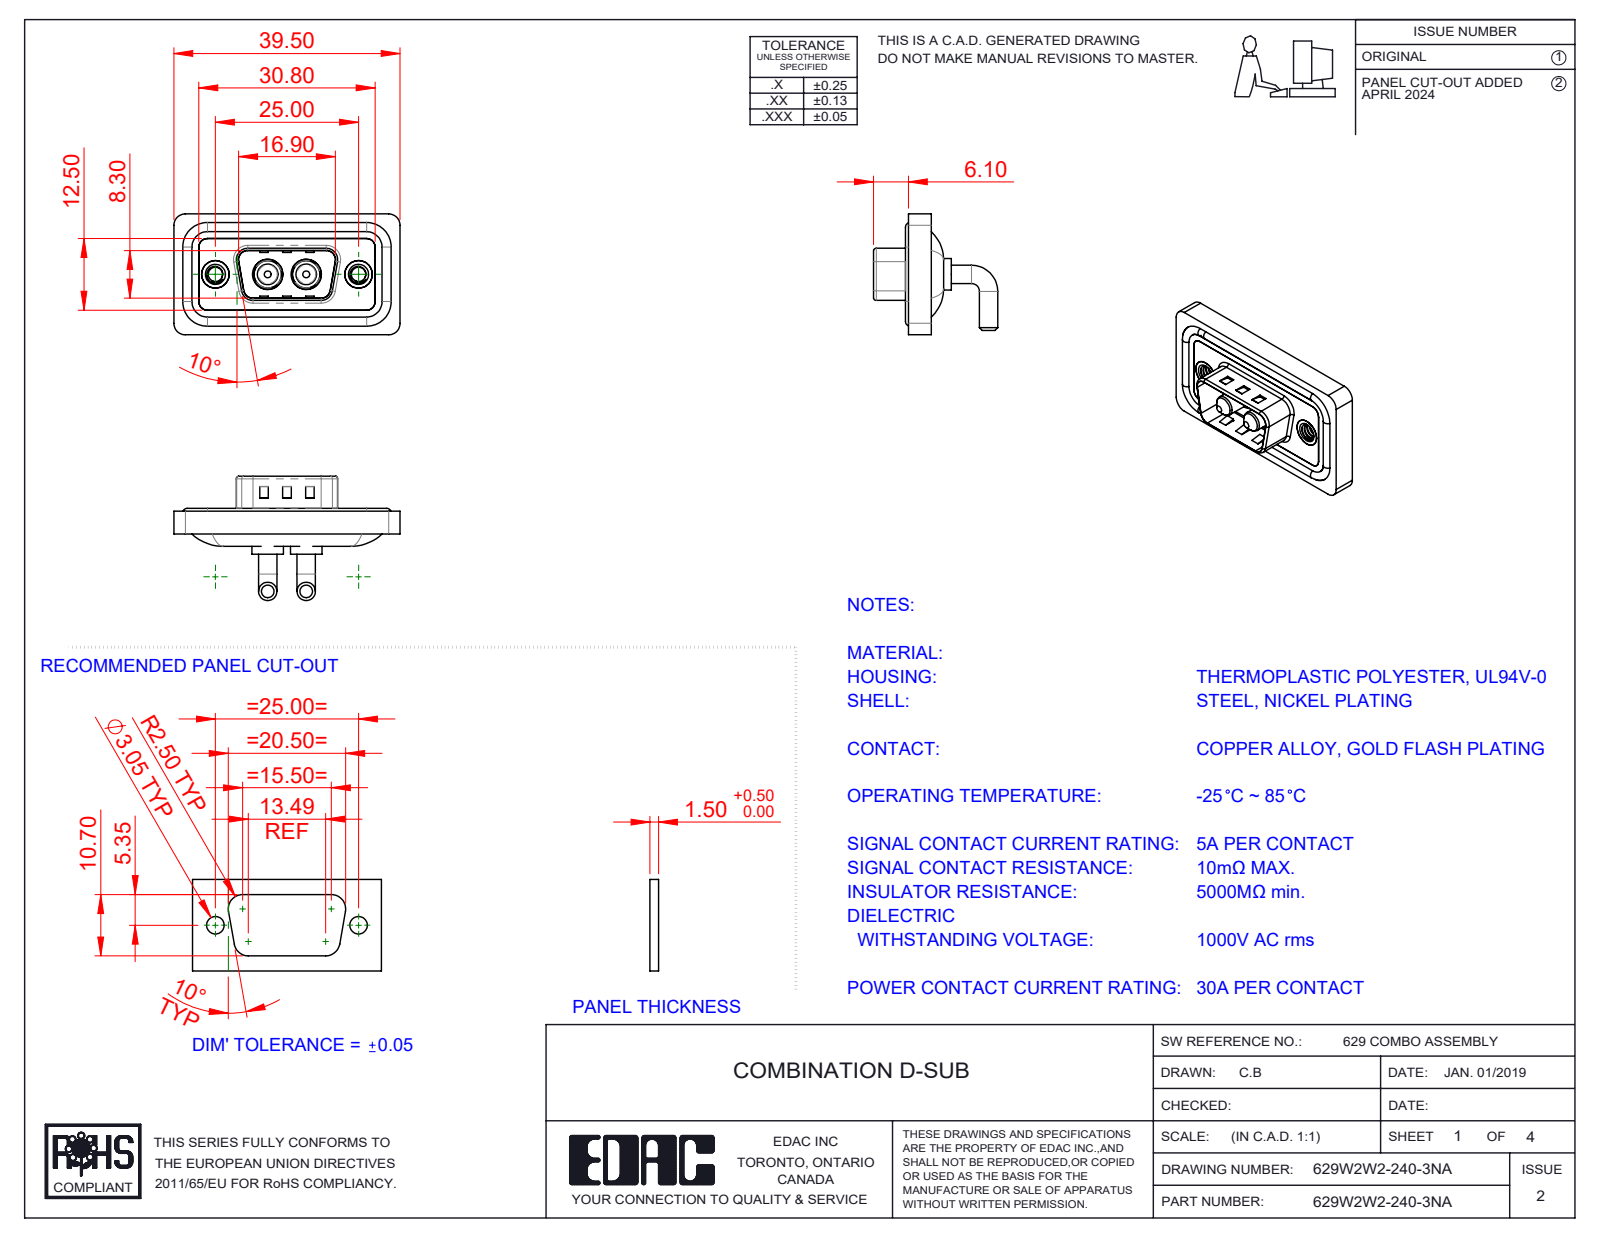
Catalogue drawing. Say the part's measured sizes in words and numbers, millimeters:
The part is named "Power Pin_30A RA; 629W2W2-240-3NA; 629Combo Shell Front_09 Contacts; 629Combo Threaded Rivet_A (+3 more)". Its 3-D file was written by "SolidWorks 2023 (CONFIG_CONTROL_DESIGN)". It is 11 solids with 491 faces: 165 planar, 220 cylindrical and 106 other. Overall it measures 39.5 by 21.7 by 21.1 millimeters. Its volume is 4 644 cubic millimeters and its surface area 7 208 square millimeters. Round holes: 2 of diameter 2.5, 2 of diameter 4, 2 of diameter 4.8, 2 of diameter 4.85, 2 of diameter 5, 2 of diameter 5.3. Round bosses or shafts: 4 of diameter 3.2, 4 of diameter 1.6, 2 of diameter 5.5, 2 of diameter 5.2, 2 of diameter 4.9, 2 of diameter 4.75, 2 of diameter 3.75, 2 of diameter 3.6. Partial cylindrical surfaces (rounded edges, fillets, slot ends): 18 of radius 1.5, 18 of radius 2, 8 of radius 0.5, 8 of radius 1.6, 4 of radius 0.25, 4 of radius 0.6, 4 of radius 0.65, 4 of radius 0.9. The main face-to-face distances are 0.4, 2.9, 1.1, 0.8, 2.1, 2.5, 3.1, 1.6, 4.5, 1.5. The hole center spacings are 9.14, 15.86, 6.72, 25.
